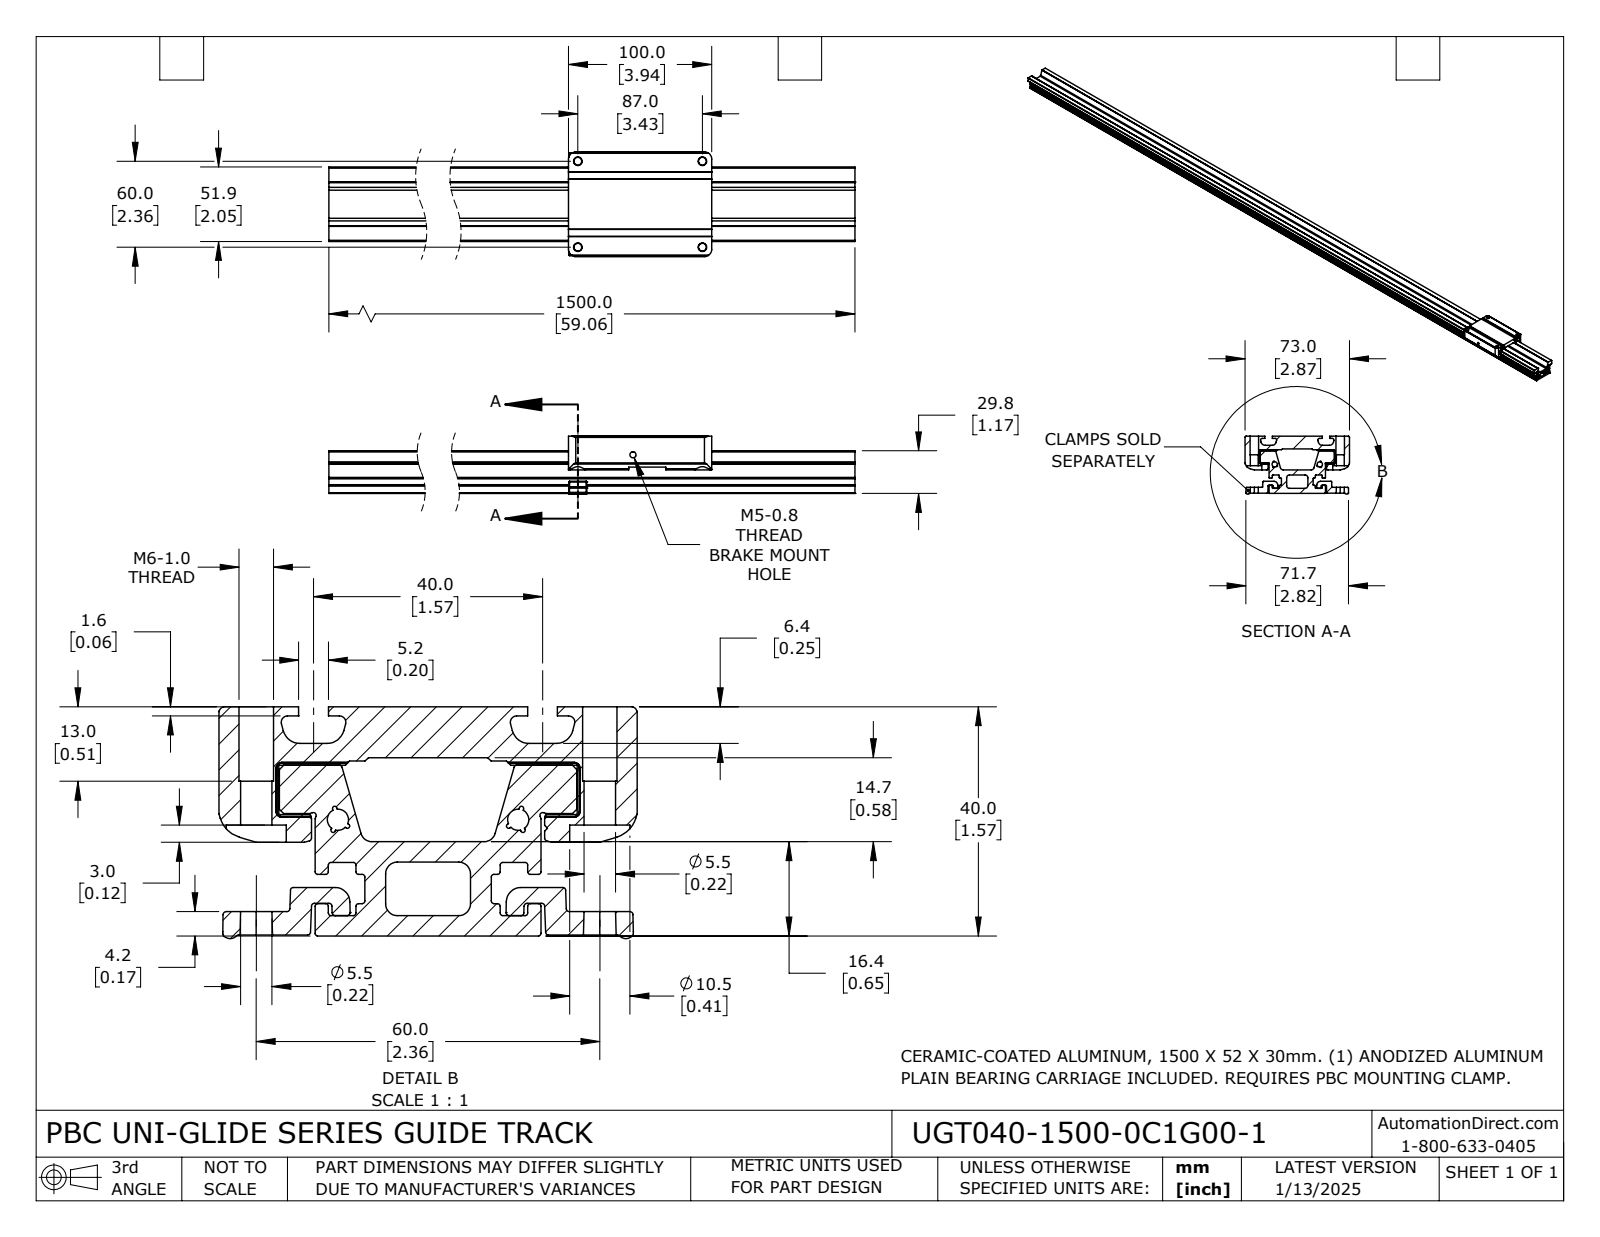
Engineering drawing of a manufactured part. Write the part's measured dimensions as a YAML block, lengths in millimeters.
part_name: "UGT040-1500-0C1G00-1_RAIL; UGT040-1500-0C1G00-1_CARRIAGE; UGT040-1500-0C1G00-1"
step_written_by: "SolidWorks 2023 (CONFIG_CONTROL_DESIGN)"
units: millimeters
bodies: {solids: 10, faces: 445, planar: 248, cylindrical: 178, other: 19}
overall_size: [1500, 73, 40]
volume: 1043000
surface_area: 497800
round_holes:
  - {diameter: 2.5, count: 4}
  - {diameter: 3, count: 4}
  - {diameter: 5.5, count: 4}
  - {diameter: 6, count: 4}
  - {diameter: 10.5, count: 4}
  - {diameter: 3.7, count: 2}
  - {diameter: 4.2, count: 1}
partial_cylinders:
  - {radius: 0.5, count: 26}
  - {radius: 1, count: 8}
  - {radius: 2.4, count: 8}
  - {radius: 0.4, count: 6}
  - {radius: 5, count: 6}
  - {radius: 0.5, count: 4}
  - {radius: 0.9, count: 4}
  - {radius: 1.1, count: 4}
face_to_face_distances: [3.6, 12.9, 29.8, 16.5, 13.4, 26.2, 39.4, 6.2, 45.7, 9.3]
hole_center_spacings: [15, 31, 41, 46, 56, 58, 59.9, 60]
